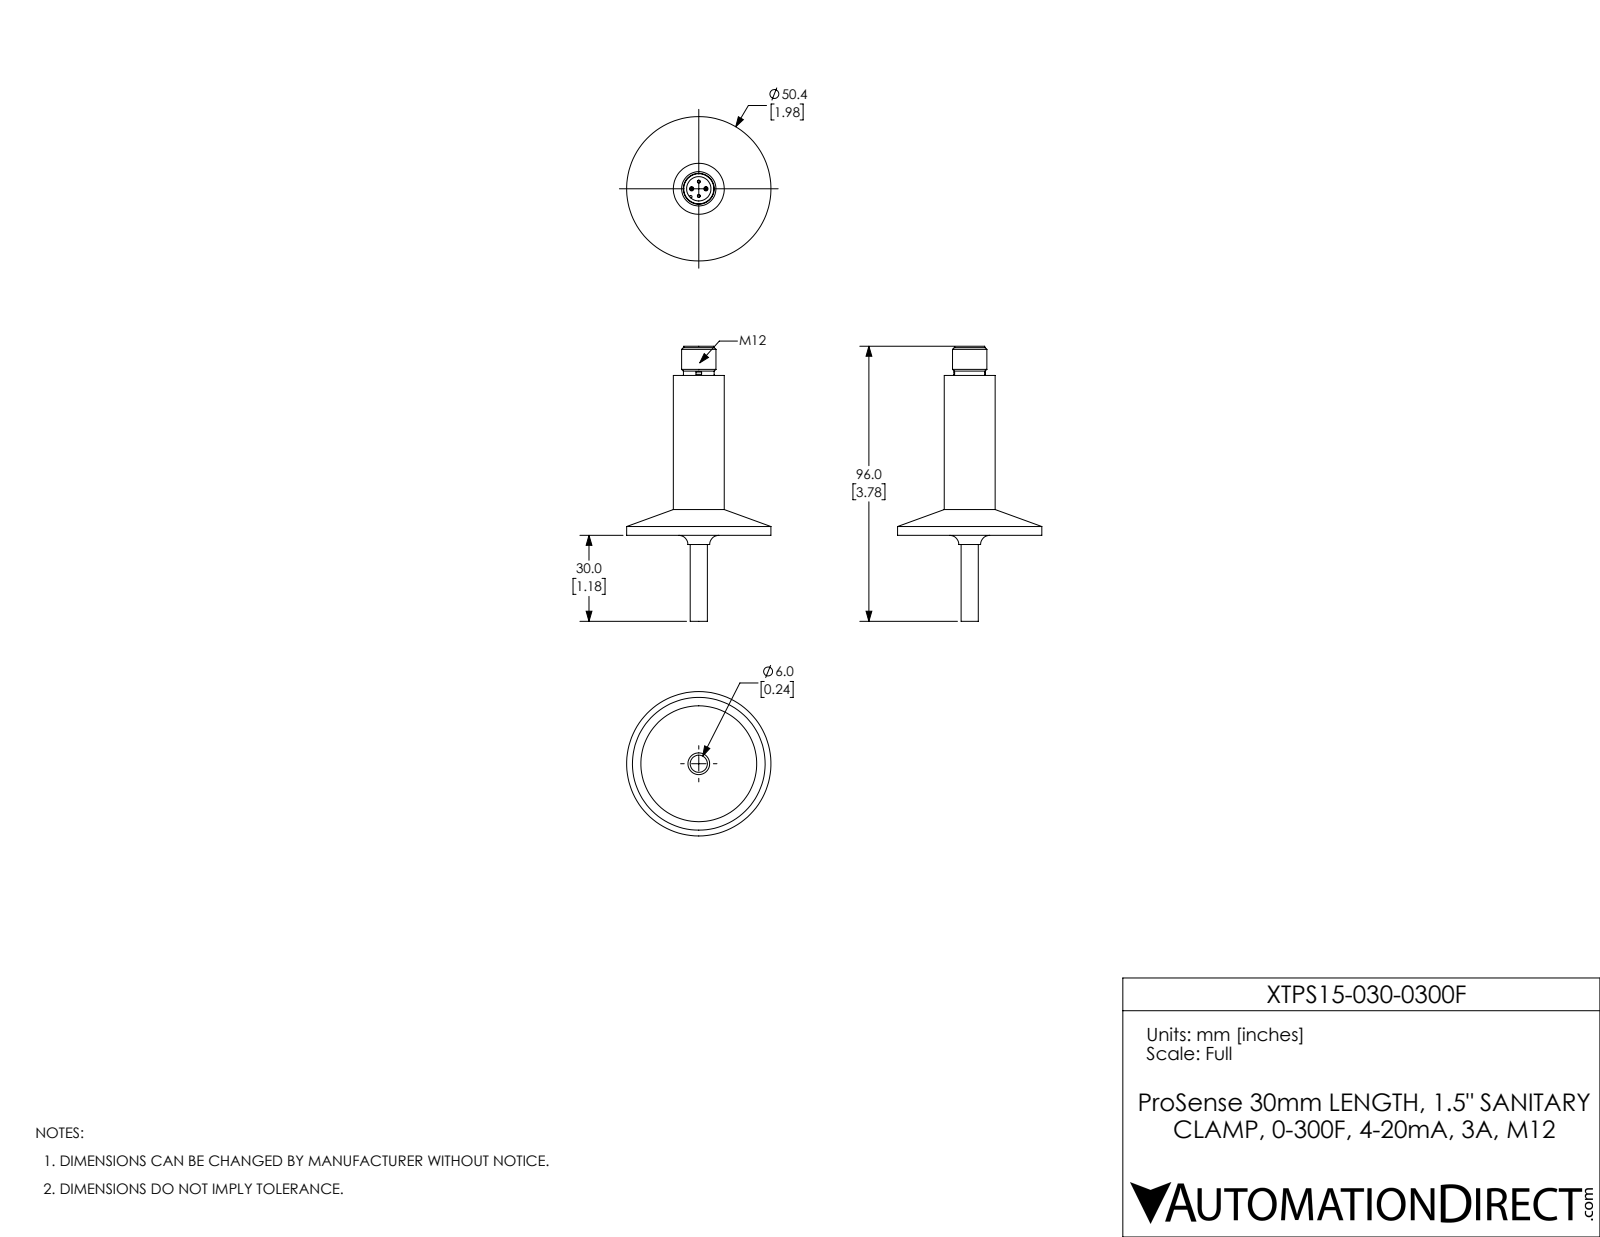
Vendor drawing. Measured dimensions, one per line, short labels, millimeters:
name: XTPS15-030-0300F
written by: SolidWorks 2017 (AUTOMOTIVE_DESIGN)
unit: mm
bodies: 1 solid, 79 faces (26 planar, 23 cylindrical, 30 other)
size: 96 × 50.4 × 50.4
volume: 24 710 mm³; area: 8 684 mm²
holes: 1× ⌀8.5
bosses: 4× ⌀1, 1× ⌀50.4, 1× ⌀17.8, 1× ⌀12, 1× ⌀10.7, 1× ⌀10.5, 1× ⌀6
rounds: 1× R0.4
face distances: 55.8, 57, 1.2, 66, 10.2, 9, 30, 85.8, 87, 96
